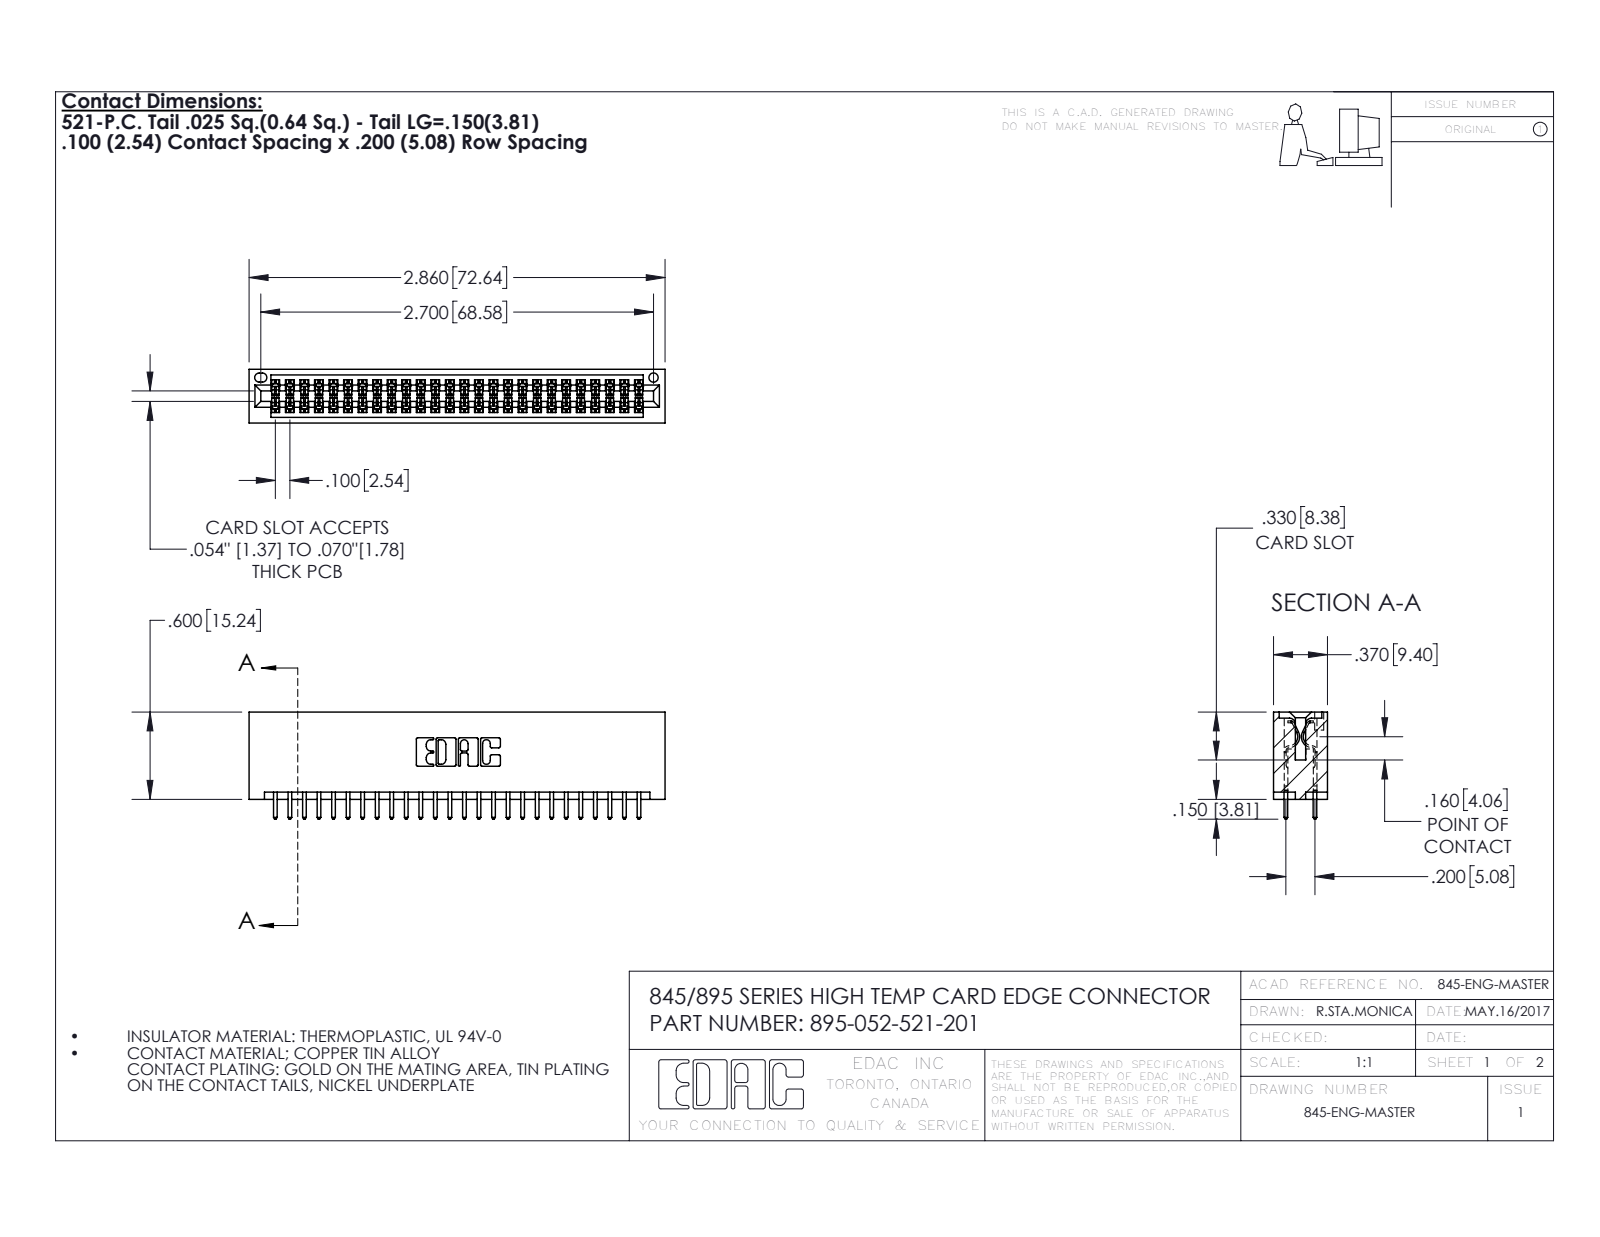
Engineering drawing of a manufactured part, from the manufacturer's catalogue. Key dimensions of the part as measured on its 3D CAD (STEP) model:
Part name (STEP PRODUCT): 395-052-521-201; 345-292-001_345-293-121; 345 Part_No Mounting Lugs
STEP written by: SolidWorks 2016 (CONFIG_CONTROL_DESIGN)
Units: inches
Bodies: 53 solids, 2718 faces (1792 planar, 926 cylindrical, 0 other)
Overall size (bounding box): 2.86 × 0.737 × 0.37
Volume: 0.458 in³ · Surface area: 16.97 in²
Round holes (diameter × count): ⌀0.064 ×1
Partial cylindrical surfaces — rounded edges, fillets, slot ends (radius × count): R0.006 ×78, R0.01 ×52, R0.01 ×22, R0.007 ×6, R0.031 ×6, R0.026 ×3, R0.014 ×2, R0.019 ×2
Main face-to-face distances: 0.298, 0.072, 0.2, 0.098, 0.272, 0.025, 0.37, 0.225, 0.175, 0.149
